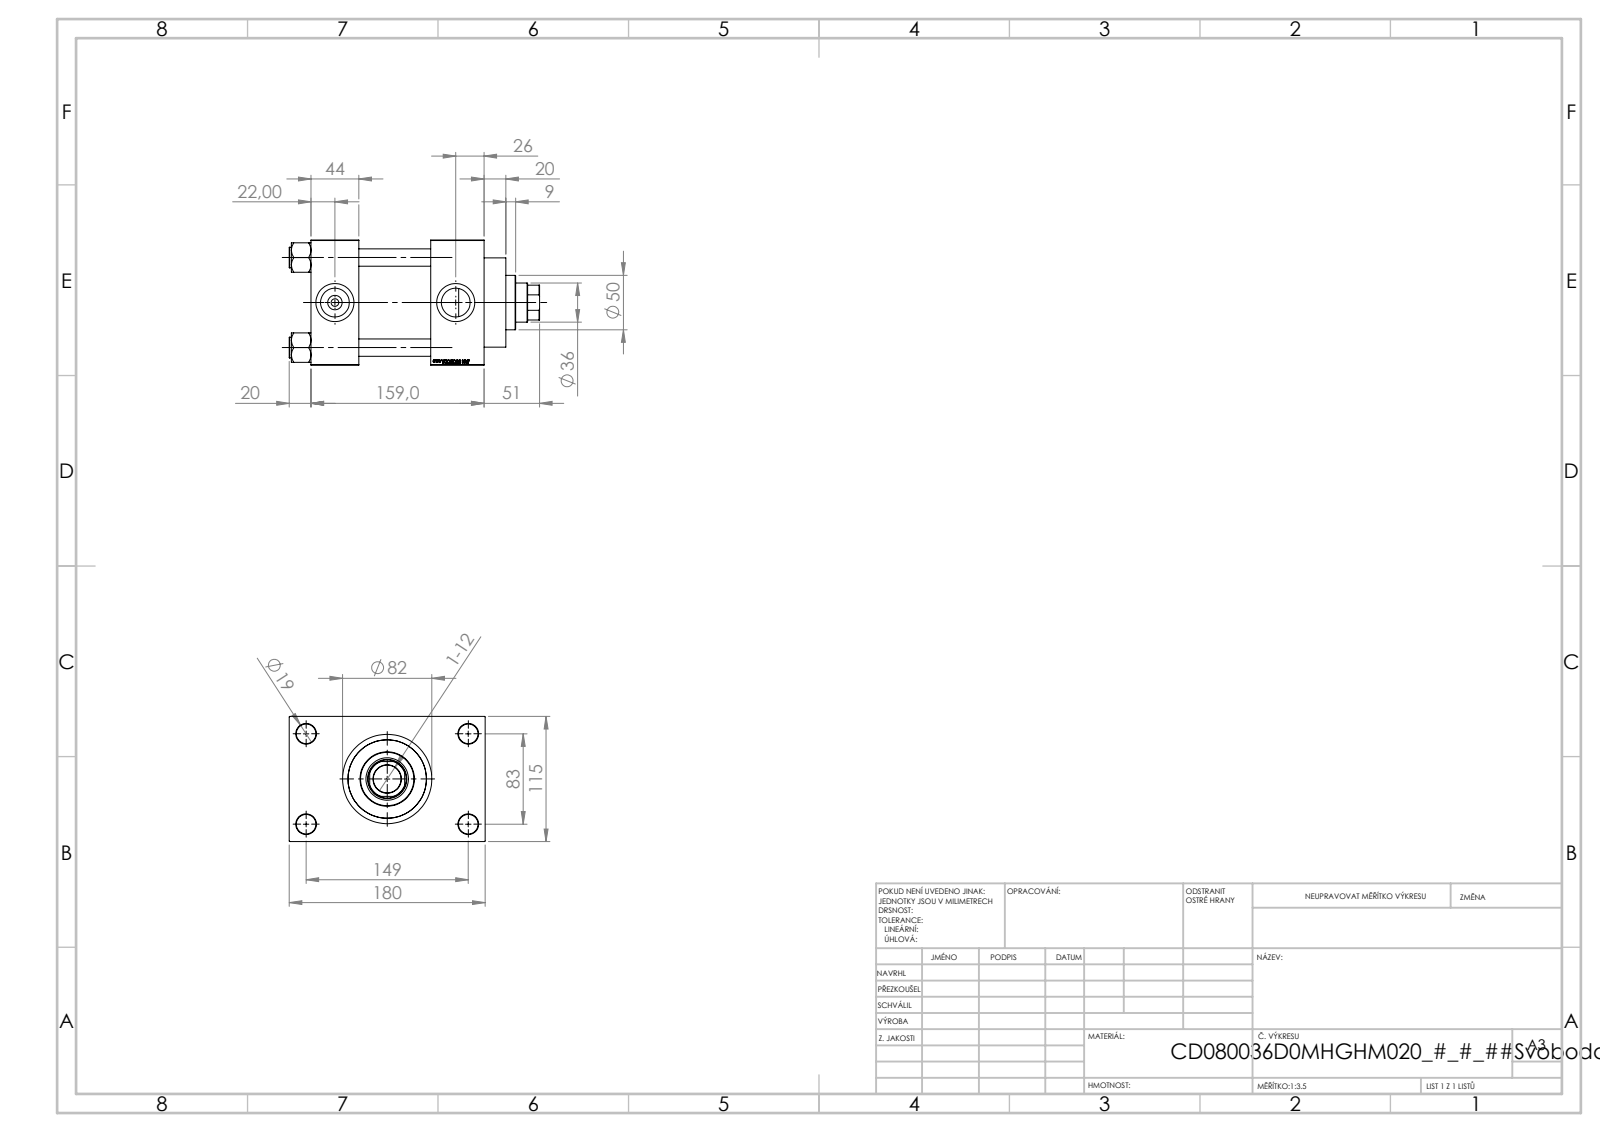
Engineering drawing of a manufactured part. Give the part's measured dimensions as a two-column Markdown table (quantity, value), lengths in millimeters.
| quantity | value |
| --- | --- |
| part name | V215CD_NUT_M5_D; V215CD_VC_A; V215CD_VCP_D; V215CD_D_TYCINKA (+1 more) |
| STEP written by | SolidWorks 2019 (CONFIG_CONTROL_DESIGN) |
| units | millimeters |
| bodies | 11 solids, 1151 faces (545 planar, 88 cylindrical, 518 other) |
| overall size | 230 × 180 × 115 |
| volume | 1 979 000 mm³ |
| surface area | 296 594 mm² |
| round holes (diameter × count) | 16 × 4, 18 × 4, 7 × 2, 26.44 × 2, 35 × 2, 25.5 × 1, 36 × 1, 39 × 1, 61 × 1, 72 × 1, 80 × 1 |
| round bosses / shafts (diameter × count) | 19 × 4, 86 × 1, 82 × 1, 50 × 1 |
| partial cylindrical surfaces (radius × count) | 17.5 × 1 |
| main face-to-face distances | 115, 66, 110, 49, 44, 159, 32.5, 147.5, 20, 69 |
| hole center spacings | 33.15, 58.48, 82.7, 85.28, 89.24, 115.85, 142.43, 83 |
